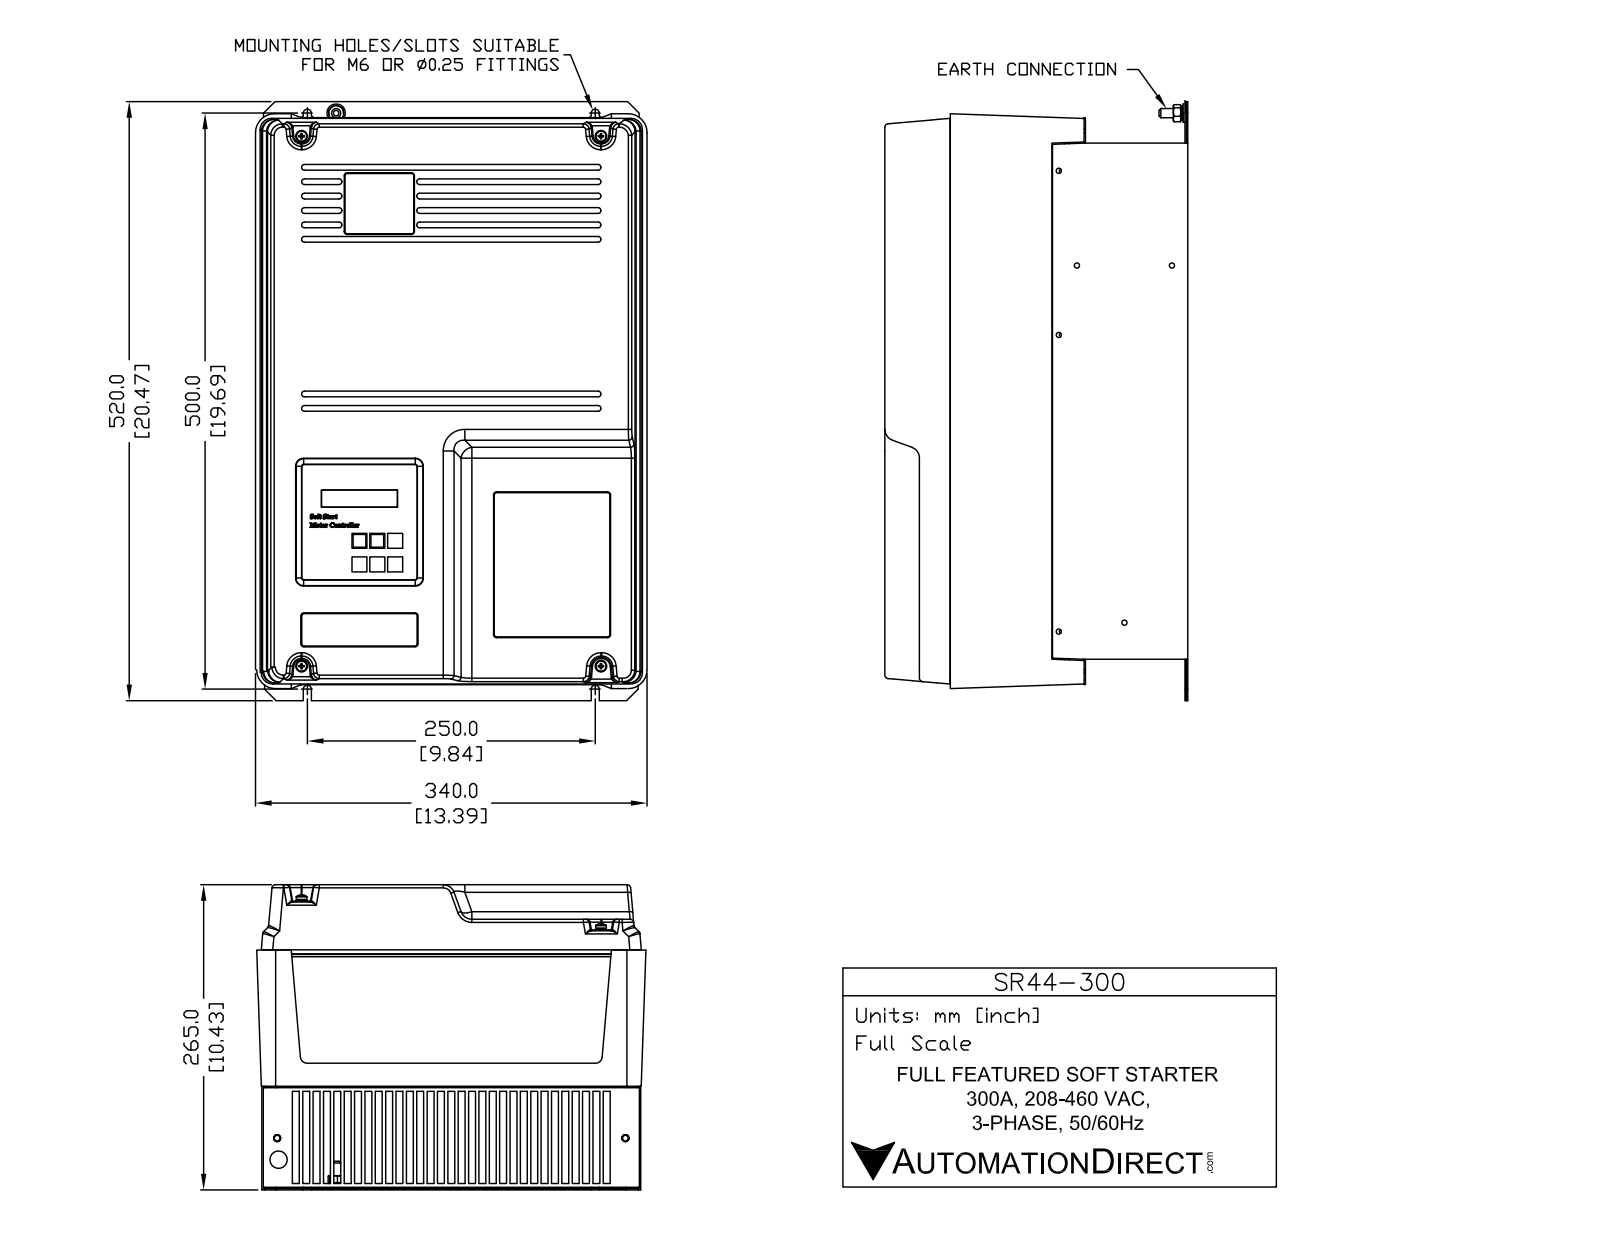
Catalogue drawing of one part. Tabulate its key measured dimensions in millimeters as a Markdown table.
| quantity | value |
| --- | --- |
| part name | SR44-300 |
| STEP written by | SolidWorks 2013 (AUTOMOTIVE_DESIGN) |
| units | millimeters |
| bodies | 1 solid, 828 faces (518 planar, 144 cylindrical, 166 other) |
| overall size | 520 × 337.91 × 263 |
| volume | 38 650 000 mm³ |
| surface area | 1 324 000 mm² |
| round holes (diameter × count) | 13 × 2 |
| round bosses / shafts (diameter × count) | 10 × 4, 16 × 1, 8 × 1 |
| partial cylindrical surfaces (radius × count) | 5 × 31, 3 × 16, 2.4 × 12, 1.5 × 8, 15 × 8, 2 × 6, 3.5 × 4, 10 × 2 |
| main face-to-face distances | 8.9, 17.8, 26.7, 35.6, 263, 5.75, 14.65, 44.5, 3.15, 23.55 |
| hole center spacings | 250 |
